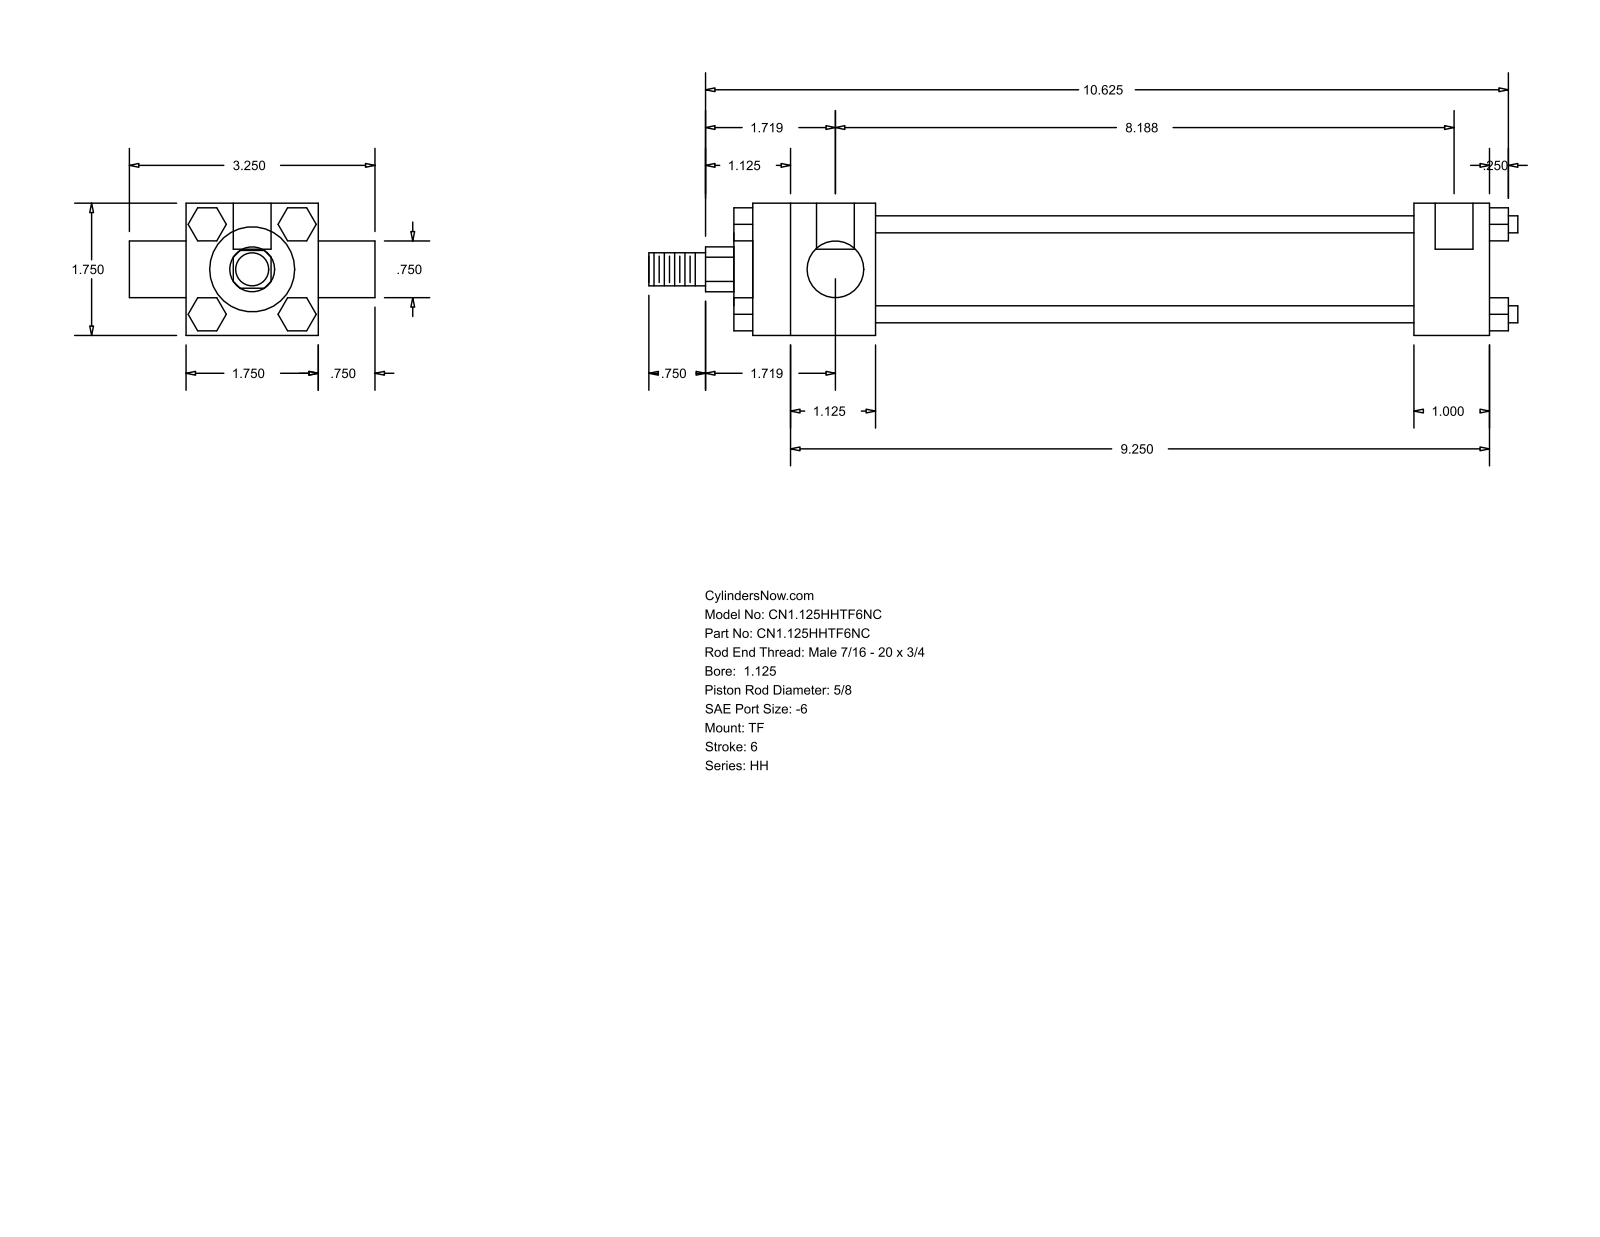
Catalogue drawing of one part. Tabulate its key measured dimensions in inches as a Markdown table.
| quantity | value |
| --- | --- |
| part name | HH_TF__0112_0.625 |
| STEP written by | GSSL Pune (CONFIG_CONTROL_DESIGN) |
| units | inches |
| bodies | 0 solids, 120 faces (92 planar, 28 cylindrical, 0 other) |
| overall size | 11.5 × 3.25 × 1.75 |
| round holes (diameter × count) | 0.219 × 3, 0.5 × 2 |
| round bosses / shafts (diameter × count) | 0.225 × 4, 1.375 × 1, 1.125 × 1, 0.75 × 1, 0.625 × 1, 0.437 × 1 |
| partial cylindrical surfaces (radius × count) | 0.297 × 1 |
| main face-to-face distances | 1.75, 0.437, 1, 7.125, 8.125, 1.625, 8.75, 9.75, 1.875, 0.25 |
| hole center spacings | 0.125, 8.063, 8.187 |
